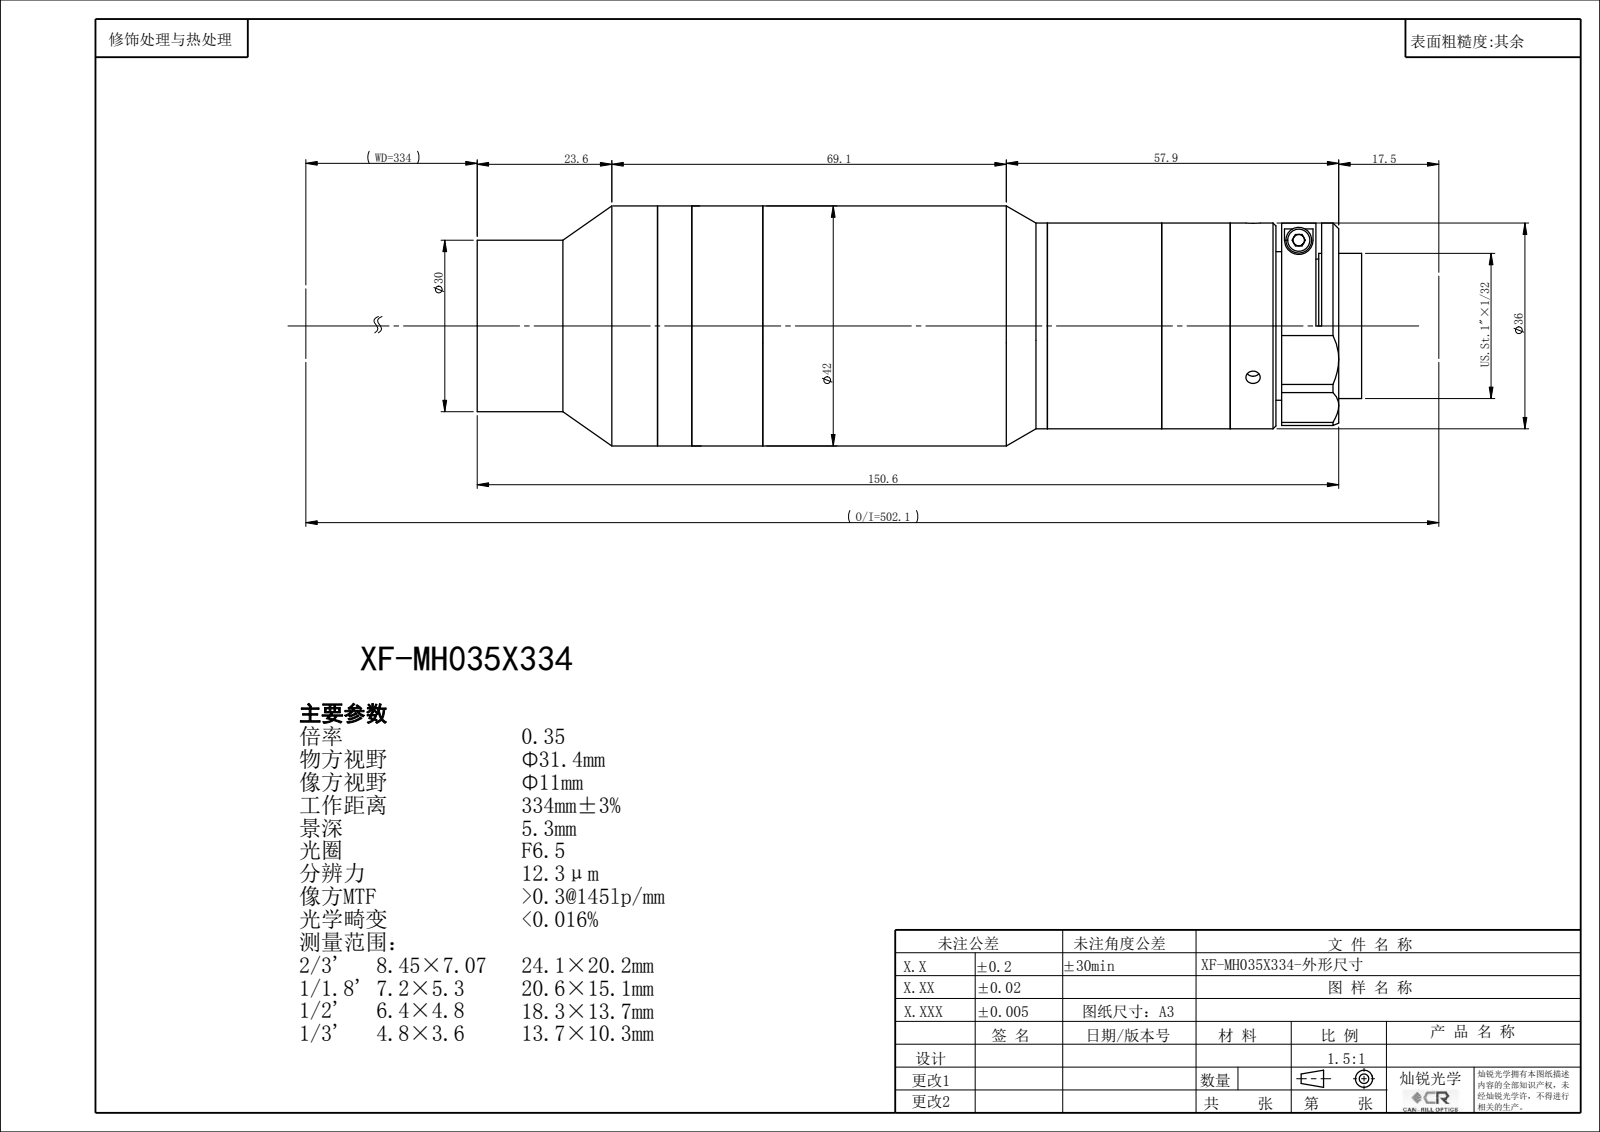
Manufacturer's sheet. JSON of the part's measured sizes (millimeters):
{"part_name": "XF-MH035X334", "step_written_by": "SolidWorks 2022 (CONFIG_CONTROL_DESIGN)", "units": "millimeters", "bodies": {"solids": 0, "faces": 135, "planar": 67, "cylindrical": 44, "other": 24}, "overall_size": [155.17, 42, 42], "round_holes": [[2.5, 3], [22.4, 1], [24, 1], [26.4, 1]], "round_bosses_or_shafts": [[42, 1], [36, 1], [34, 1], [30, 1], [25.4, 1]], "face_to_face_distances": [1.5, 49.84, 51.34, 49.83, 99.67, 101.17, 98.33, 48.5, 1.34, 2.84]}
